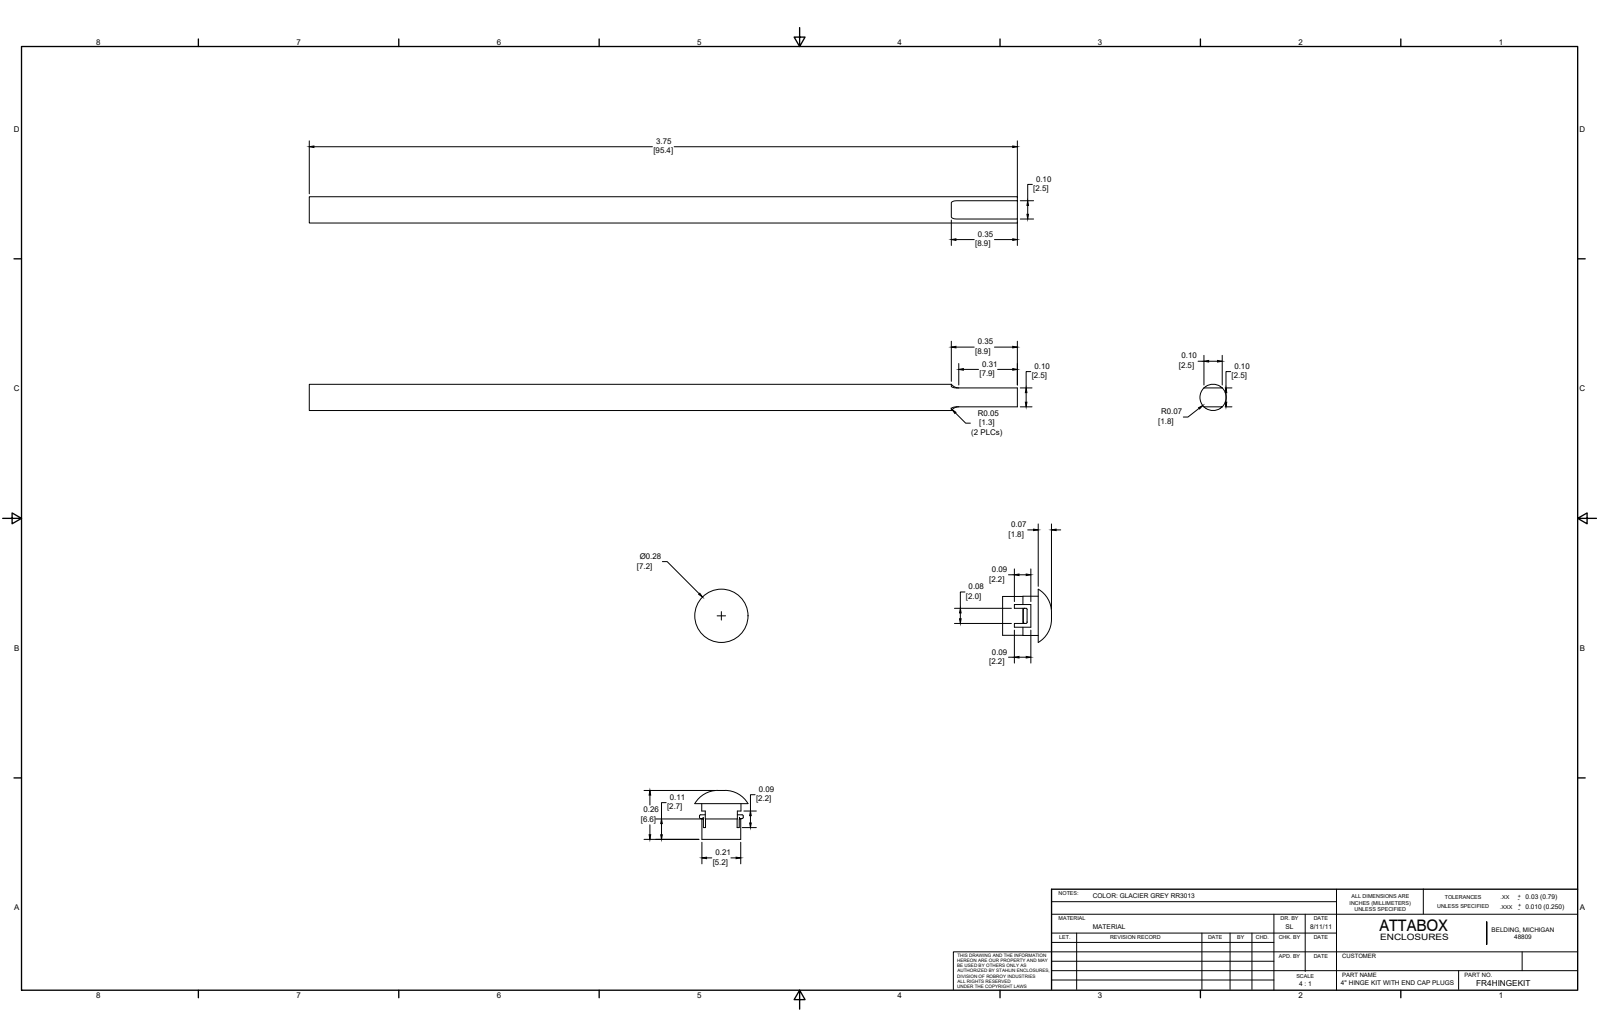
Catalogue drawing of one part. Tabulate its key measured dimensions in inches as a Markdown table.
| quantity | value |
| --- | --- |
| part name | FR4HINGEKIT |
| STEP written by | SolidWorks 2019 (AUTOMOTIVE_DESIGN) |
| units | inches |
| bodies | 6 solids, 252 faces (136 planar, 86 cylindrical, 30 other) |
| overall size | 3.883 × 2.361 × 1.389 |
| volume | 0.129 in³ |
| surface area | 4.673 in² |
| round holes (diameter × count) | 0.131 × 4 |
| round bosses / shafts (diameter × count) | 0.208 × 4, 0.206 × 4, 0.135 × 2 |
| partial cylindrical surfaces (radius × count) | 0.006 × 32, 0.008 × 12, 0.401 × 4 |
| main face-to-face distances | 0.093, 0.096, 0.189, 0.598, 0.595, 0.502, 0.02, 0.1, 0.817, 0.15 |
| hole center spacings | 0.407, 0.522, 0.831, 0.859, 1.093, 1.499 |
